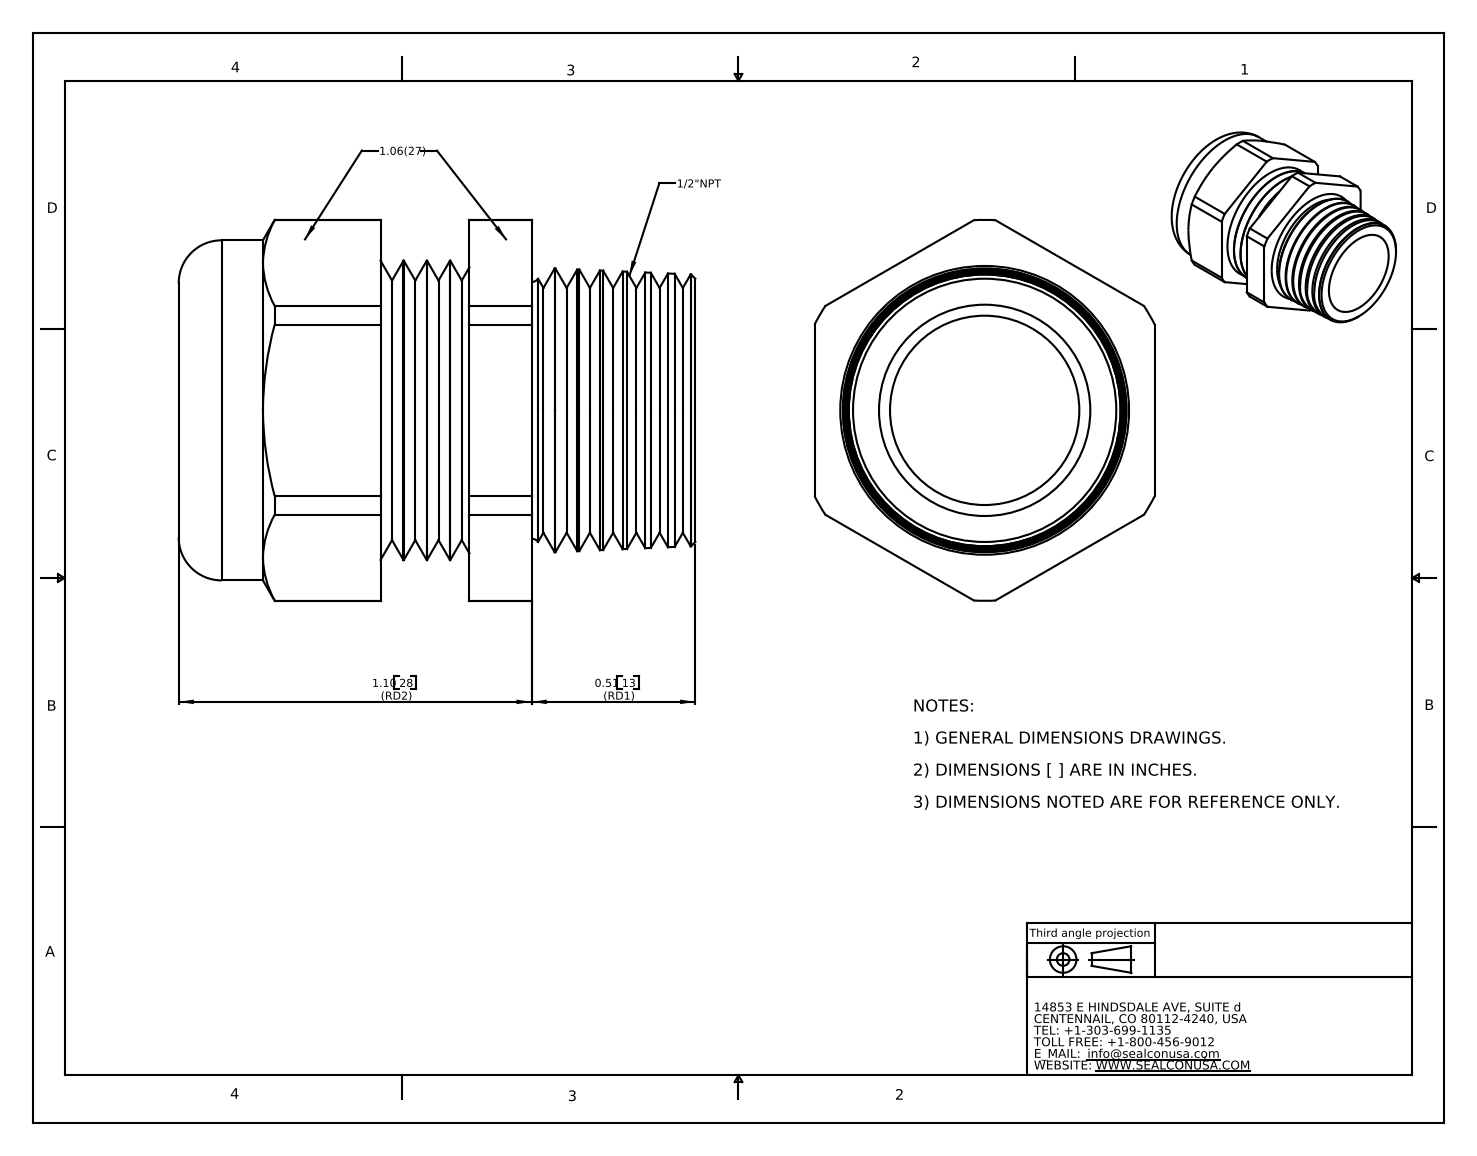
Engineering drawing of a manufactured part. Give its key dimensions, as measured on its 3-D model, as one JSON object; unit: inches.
{"part_name": "CD16NA-GY", "step_written_by": "SolidWorks 2007 (CONFIG_CONTROL_DESIGN)", "units": "inches", "bodies": {"solids": 2, "faces": 126, "planar": 20, "cylindrical": 30, "other": 76}, "overall_size": [1.61, 1.187, 1.06], "volume_in3": 0.718, "surface_area_in2": 13.23, "round_holes": [[0.59, 1], [0.757, 1]], "round_bosses_or_shafts": [[1.06, 1], [0.933, 1]], "partial_cylinders_radius": [[0.594, 1]], "face_to_face_distances": [1.06, 0.837, 0.643, 0.194, 0.367, 0.277, 0.471, 1.347, 0.981, 0.704]}
